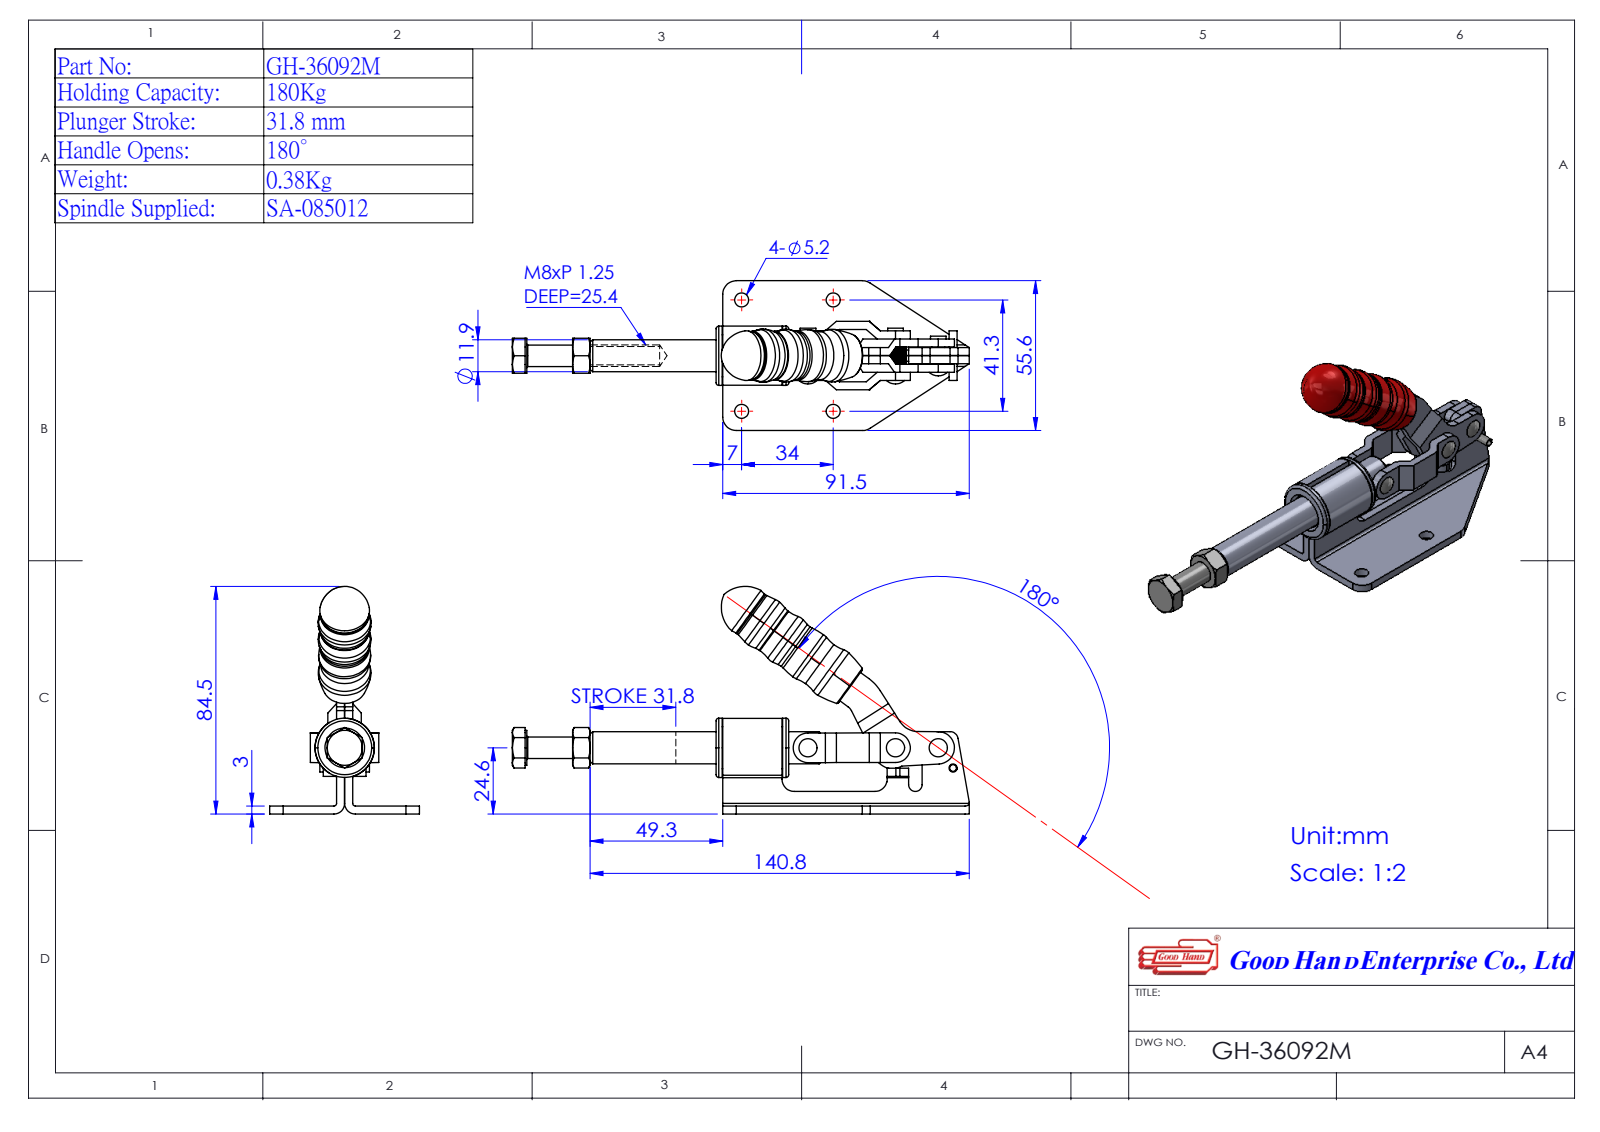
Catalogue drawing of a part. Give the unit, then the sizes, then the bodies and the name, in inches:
Units: inches
Overall size (bounding box): 6.651 × 3.327 × 2.189
Round holes (diameter × count): ⌀0.205 ×4, ⌀0.157 ×3, ⌀0.098 ×1, ⌀0.268 ×1, ⌀0.469 ×1
Round bosses / shafts (diameter × count): ⌀0.23 ×3, ⌀0.866 ×1, ⌀0.614 ×1, ⌀0.512 ×1, ⌀0.315 ×1, ⌀0.118 ×1
Partial cylindrical surfaces — rounded edges, fillets, slot ends (radius × count): R0.157 ×7, R0.039 ×2, R0.039 ×2, R0.118 ×2, R0.177 ×2, R0.197 ×2, R0.217 ×2, R0.431 ×2
Main face-to-face distances: 0.118, 0.236, 0.126, 0.362, 0.244, 0.488, 0.37, 0.256, 0.138, 0.626
Hole centre spacings: 1.339, 1.626, 2.106, 0.366, 0.625, 0.893, 1.28, 1.905
Volume: 3.574 in³ · Surface area: 51.98 in²
Bodies: 5 solids, 505 faces (123 planar, 168 cylindrical, 214 other)
Part name (STEP PRODUCT): Group1^GH-36092M(簡化); Group5^GH-36092M(簡化); 436092M33-1^GH-36092M(簡化); Group2^GH-36092M(簡化) (+2 more)
STEP written by: SolidWorks 2016 (AUTOMOTIVE_DESIGN)
